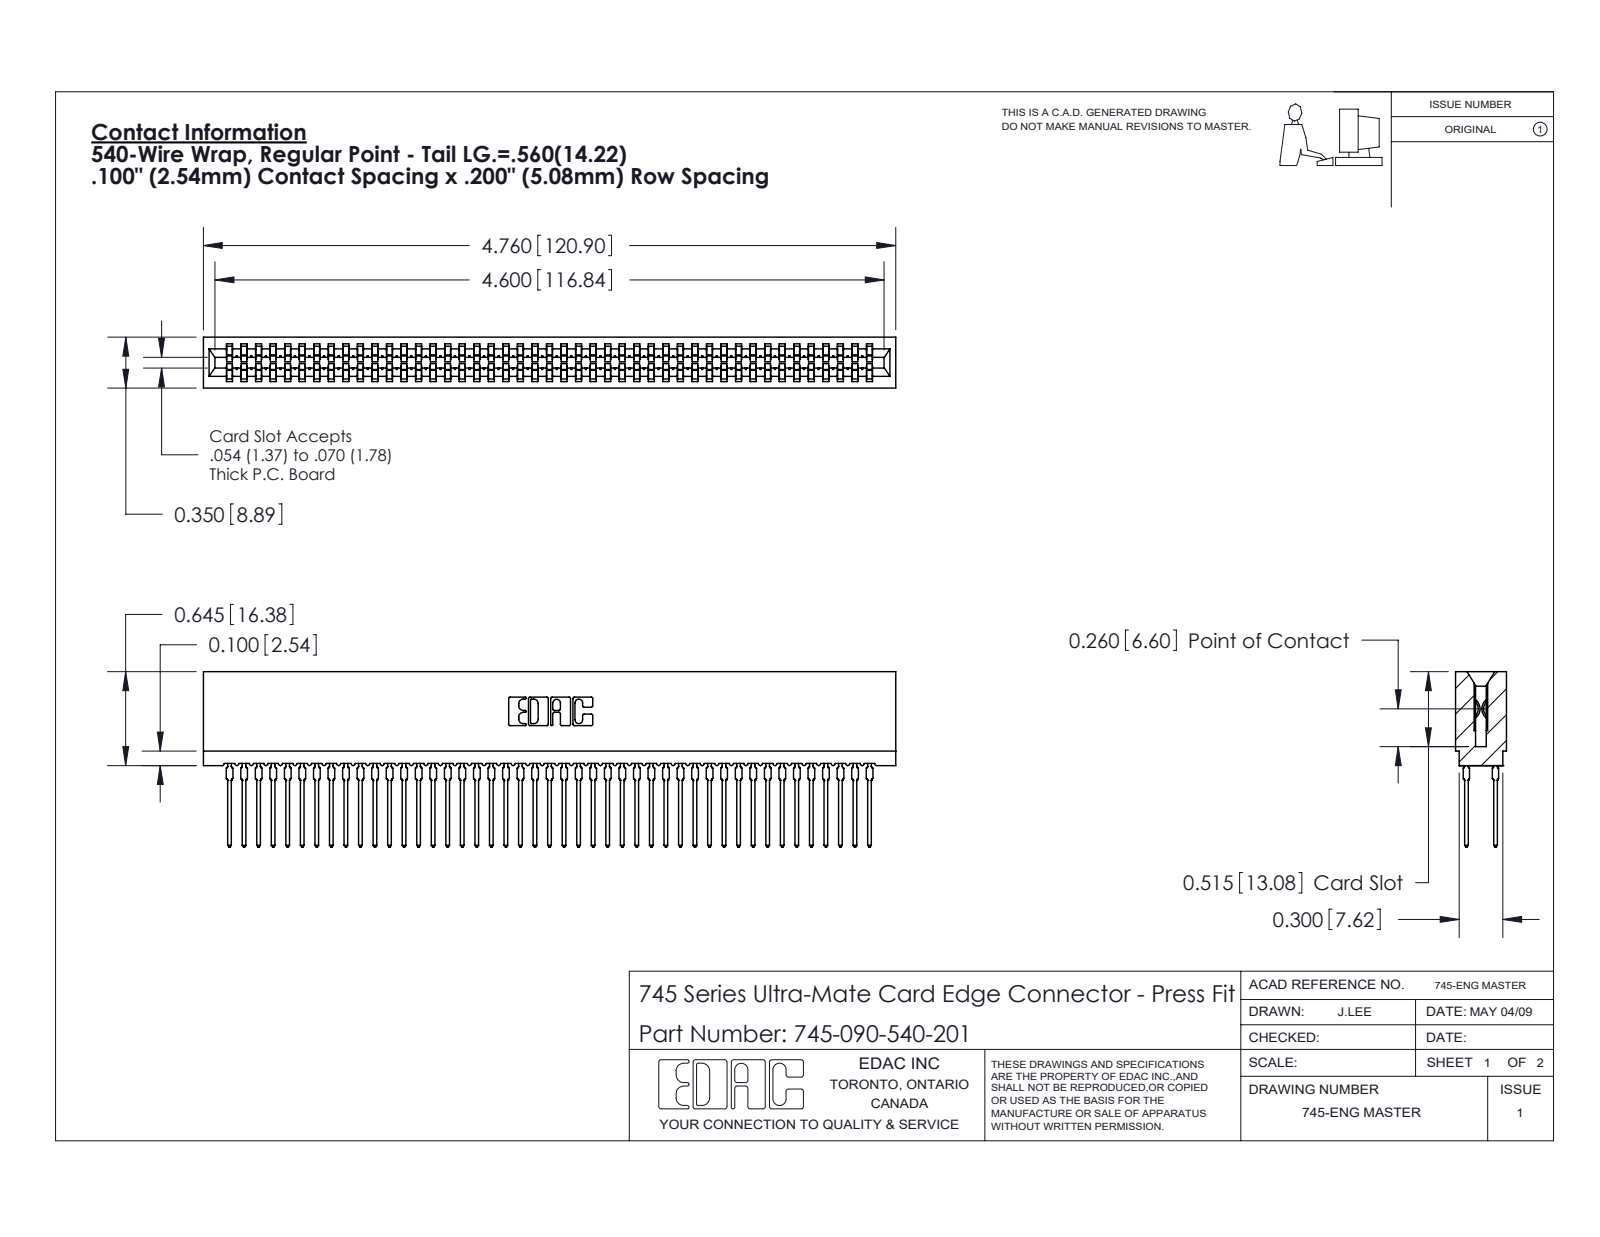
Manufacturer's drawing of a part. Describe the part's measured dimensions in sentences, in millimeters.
The part is named "745-090-540-201; 745-292-001_540; 745 Part_Insulator Option - 01". Its 3-D file was written by "SolidWorks 2020 (CONFIG_CONTROL_DESIGN)". It is 91 solids with 8150 faces: 4195 planar, 1615 cylindrical and 2340 other. Overall it measures 120.9 by 30.6 by 8.9 millimeters. Its volume is 11 100 cubic millimeters and its surface area 23 750 square millimeters. Partial cylindrical surfaces (rounded edges, fillets, slot ends): 180 of radius 0.5, 90 of radius 0.4, 22 of radius 0.3, 8 of radius 0.1, 8 of radius 0.3, 6 of radius 0.2, 6 of radius 0.8, 3 of radius 0.7. The main face-to-face distances are 1.6, 7.3, 8.9, 5.1, 1.1, 7.7, 0.5, 6.2, 3.5, 5.4.
